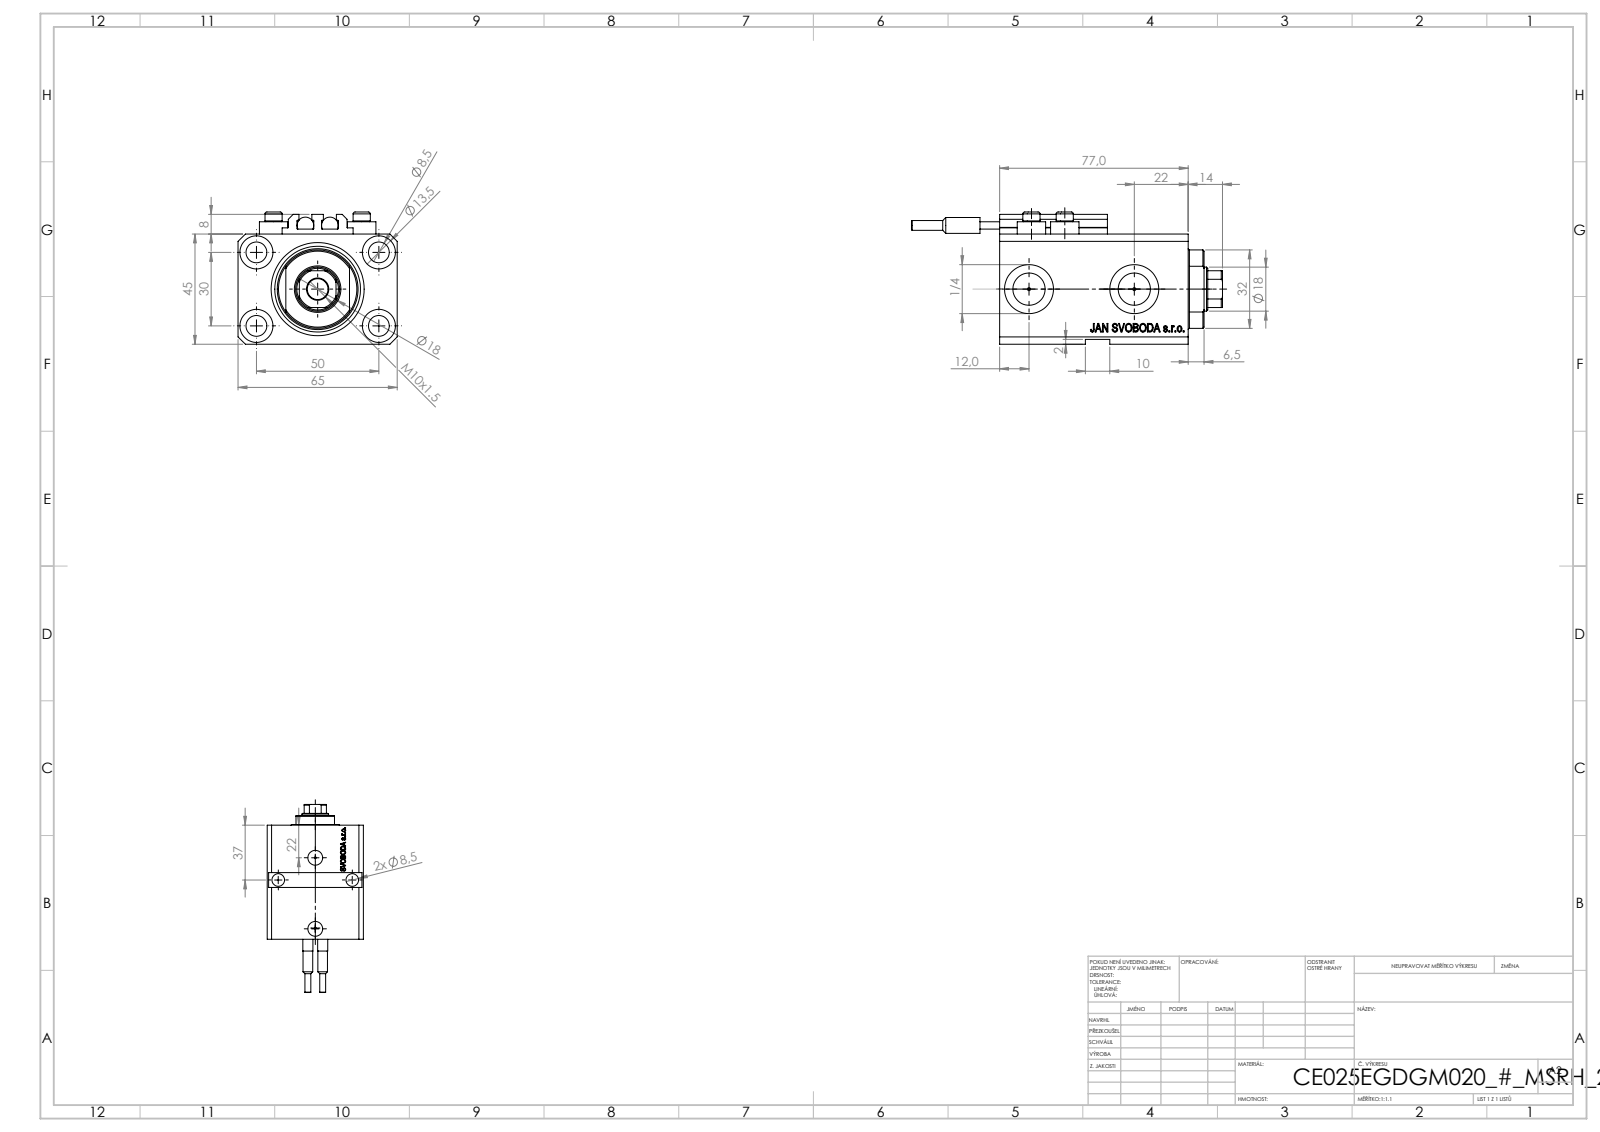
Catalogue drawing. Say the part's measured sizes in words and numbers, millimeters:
The part is named "V250CE_C_VCP; ALLEN BOLT V250CE; V250CE_E_Body; V250CE_VC_E (+1 more)". Its 3-D file was written by "SolidWorks 2019 (CONFIG_CONTROL_DESIGN)". It is 10 solids with 1135 faces: 547 planar, 150 cylindrical and 438 other. Overall it measures 127 by 65 by 54 millimeters. Its volume is 199 731 cubic millimeters and its surface area 63 072 square millimeters. Round holes: 7 of diameter 8.5, 4 of diameter 1.25, 4 of diameter 4, 4 of diameter 13.5, 2 of diameter 10, 2 of diameter 13.16, 2 of diameter 20, 1 of diameter 18, 1 of diameter 25, 1 of diameter 38. Round bosses or shafts: 4 of diameter 11.6, 4 of diameter 7, 2 of diameter 6.8, 2 of diameter 6.5, 2 of diameter 4. Partial cylindrical surfaces (rounded edges, fillets, slot ends): 10 of radius 0.2, 1 of radius 8.5, 1 of radius 16. The main face-to-face distances are 45, 65, 63, 2, 14, 3, 77, 47, 5, 6.9. The hole center spacings are 29.15, 50, 13.6, 15.12, 18.81, 18.97, 26.22, 26.61.
